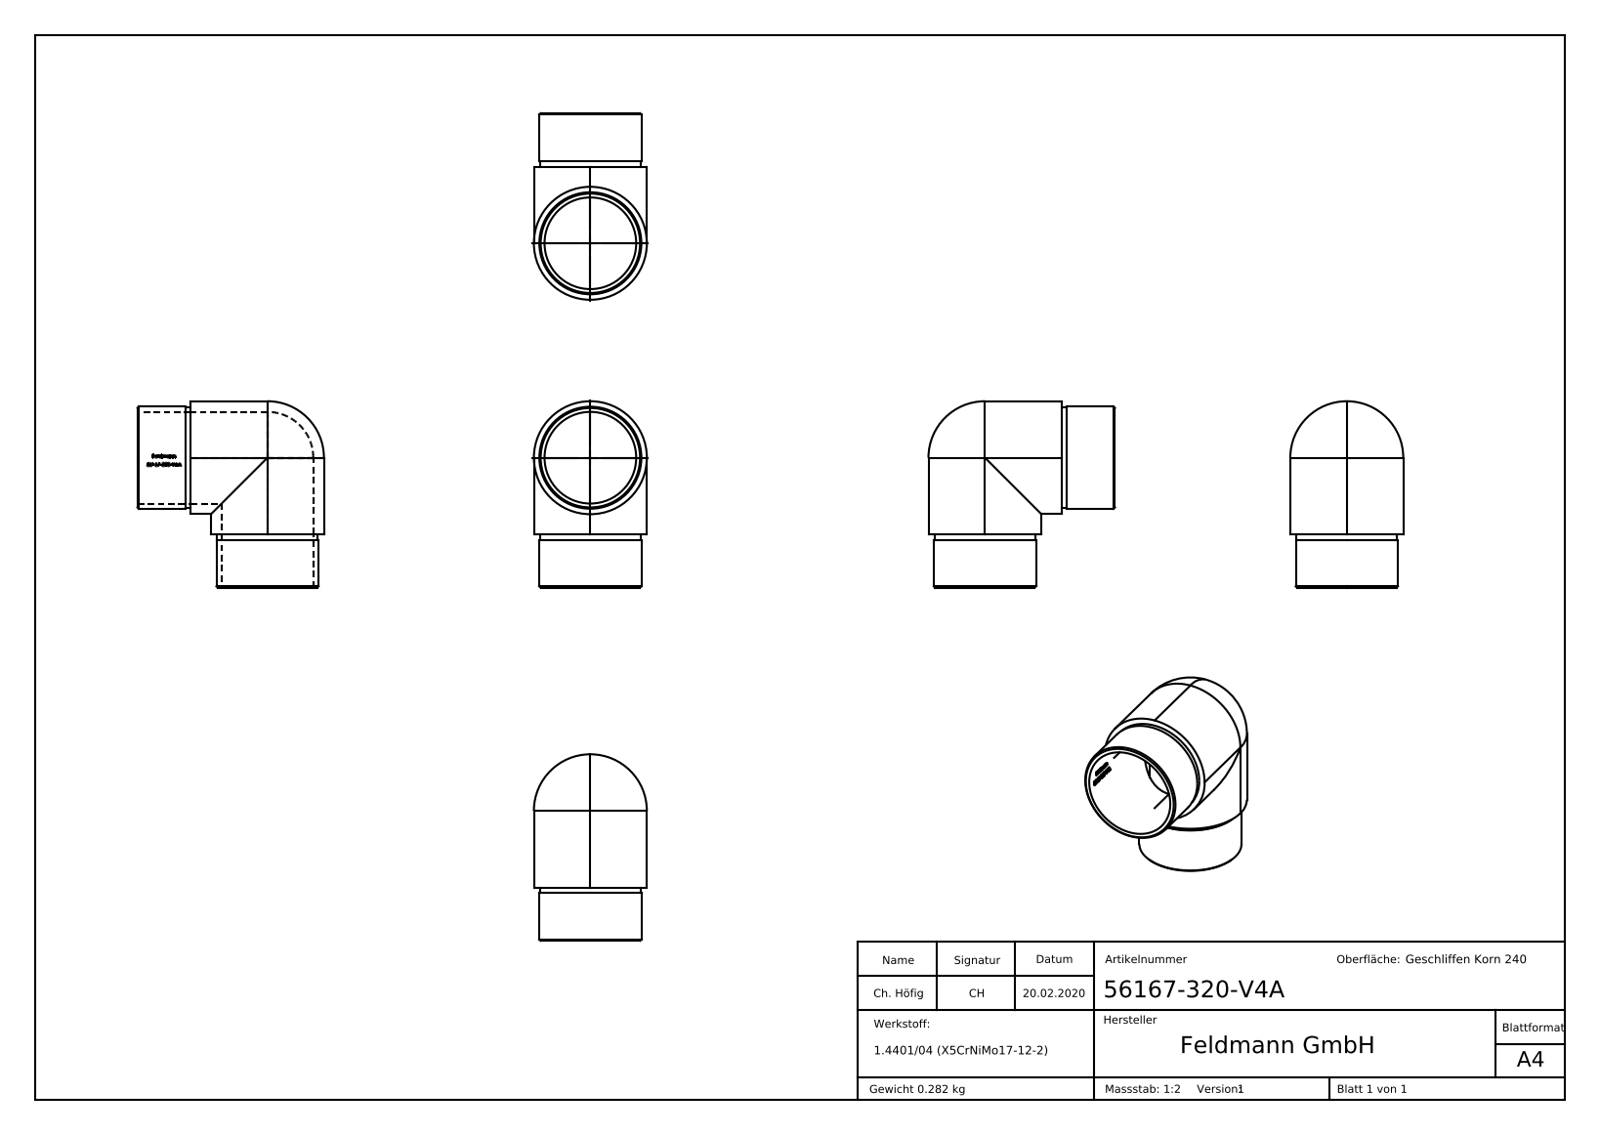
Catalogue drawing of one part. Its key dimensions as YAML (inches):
part_name: "56167-320-V4A"
step_written_by: "SolidWorks 2015 (CONFIG_CONTROL_DESIGN)"
units: inches
bodies: {solids: 1, faces: 250, planar: 94, cylindrical: 38, other: 118}
overall_size: [2.756, 2.756, 1.669]
volume: 2.154
surface_area: 36.31
round_holes:
  - {diameter: 1.354, count: 2}
round_bosses_or_shafts:
  - {diameter: 1.669, count: 2}
  - {diameter: 1.508, count: 2}
  - {diameter: 1.492, count: 2}
partial_cylinders:
  - {radius: 0.697, count: 1}
face_to_face_distances: [0.787, 0.709, 0.079, 0.015, 0.05, 0.117, 0.167, 0.052, 0.144, 0.129]
